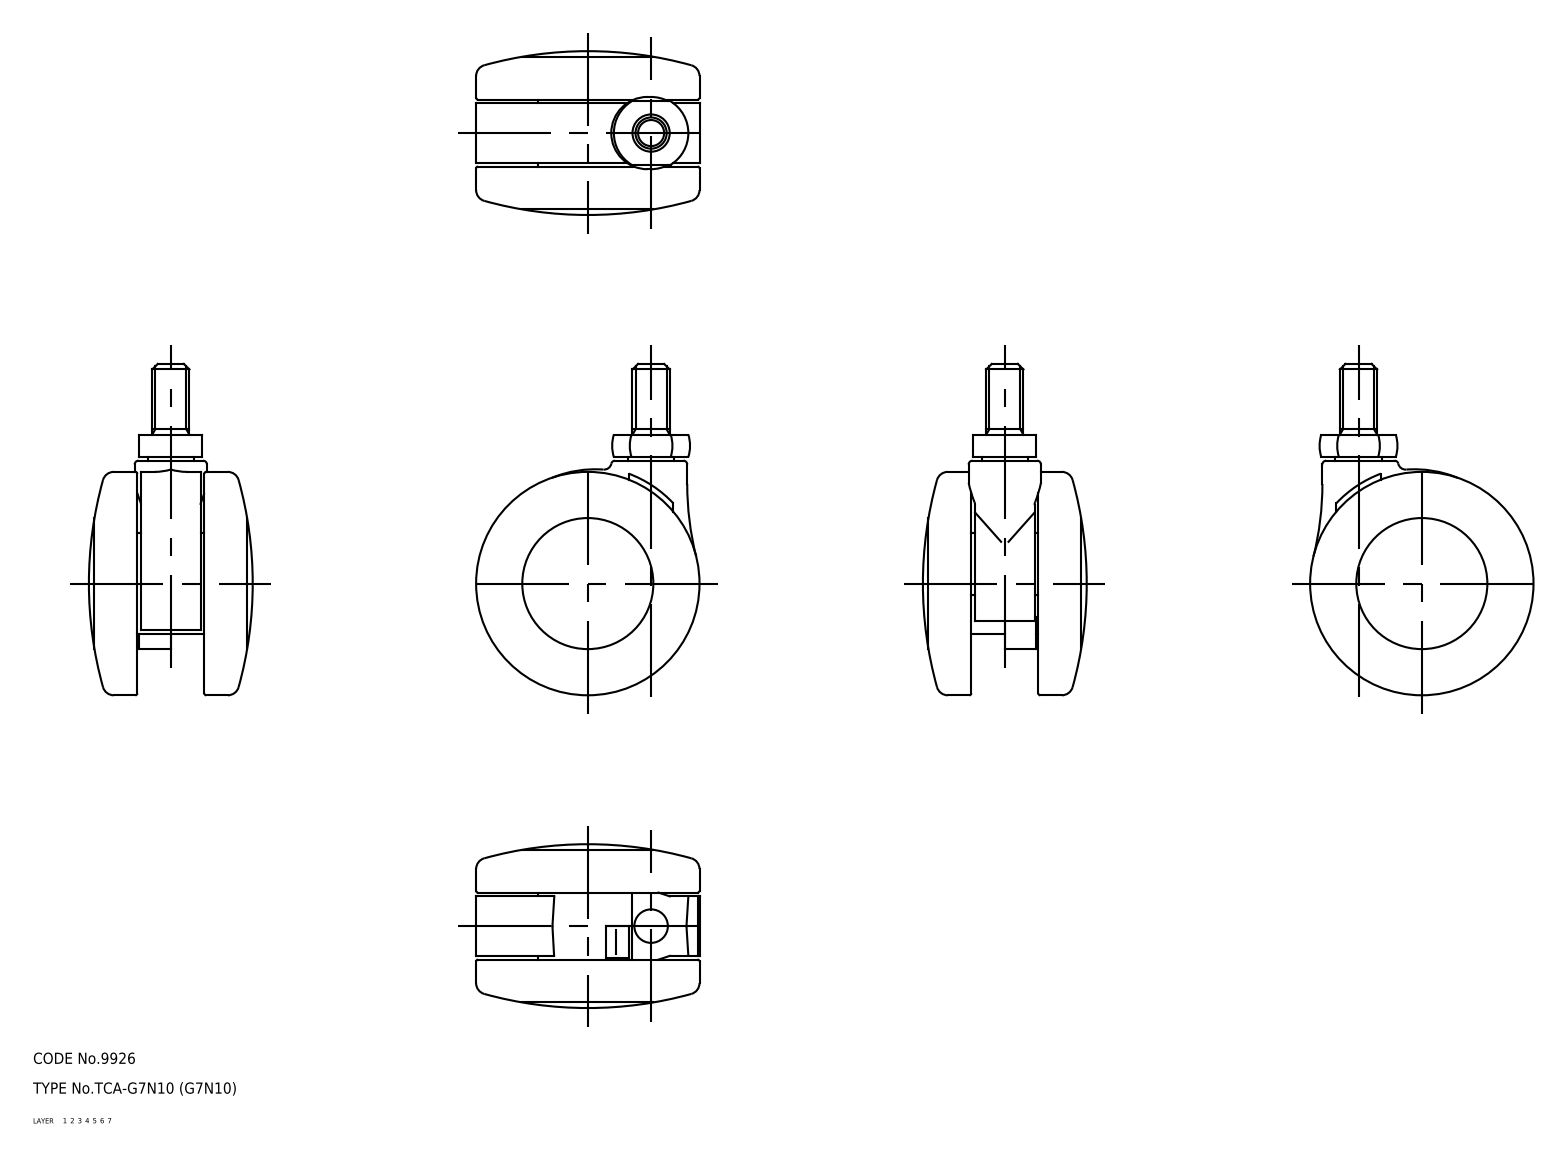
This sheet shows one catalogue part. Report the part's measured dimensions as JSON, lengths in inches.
{"part_name": "wheel; main shaft; G7N10_12926_36", "step_written_by": "CADfix (AUTOMOTIVE_DESIGN)", "units": "inches", "bodies": {"solids": 4, "faces": 129, "planar": 0, "cylindrical": 0, "other": 129}, "overall_size": [3.504, 2.362, 1.732], "volume_in3": 5.661, "surface_area_in2": 50.9}
